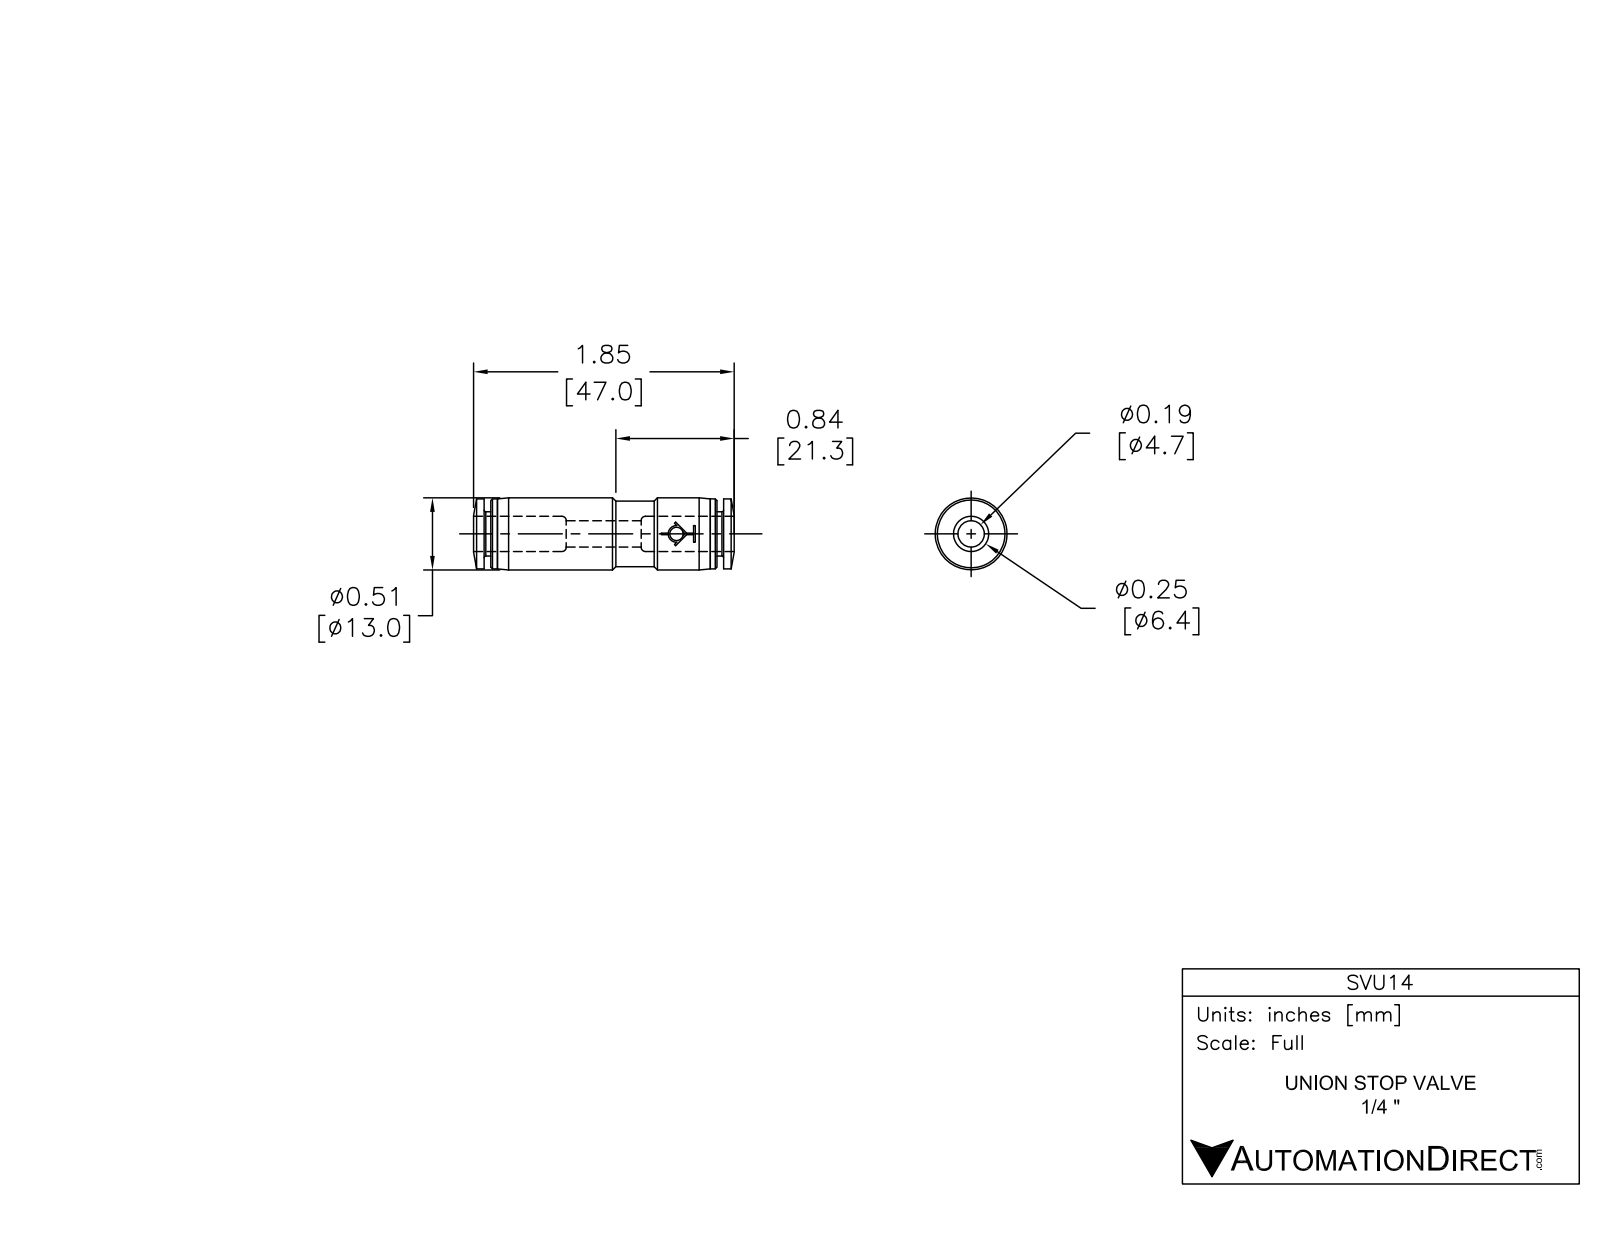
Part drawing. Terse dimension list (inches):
name: SVU14
written by: SolidWorks 2015 (AUTOMOTIVE_DESIGN)
unit: in
bodies: 1 solid, 84 faces (22 planar, 30 cylindrical, 32 other)
size: 1.846 × 0.516 × 0.512
volume: 0.268 in³; area: 4.947 in²
holes: 1× ⌀0.094, 1× ⌀0.177, 1× ⌀0.258
bosses: 1× ⌀0.512, 1× ⌀0.496, 1× ⌀0.465, 1× ⌀0.313
rounds: 1× R0.059, 1× R0.26
face distances: 0.047, 1.65, 1.697, 1.602, 0.587, 1.11, 0.539, 1.063, 0.524, 1.496
